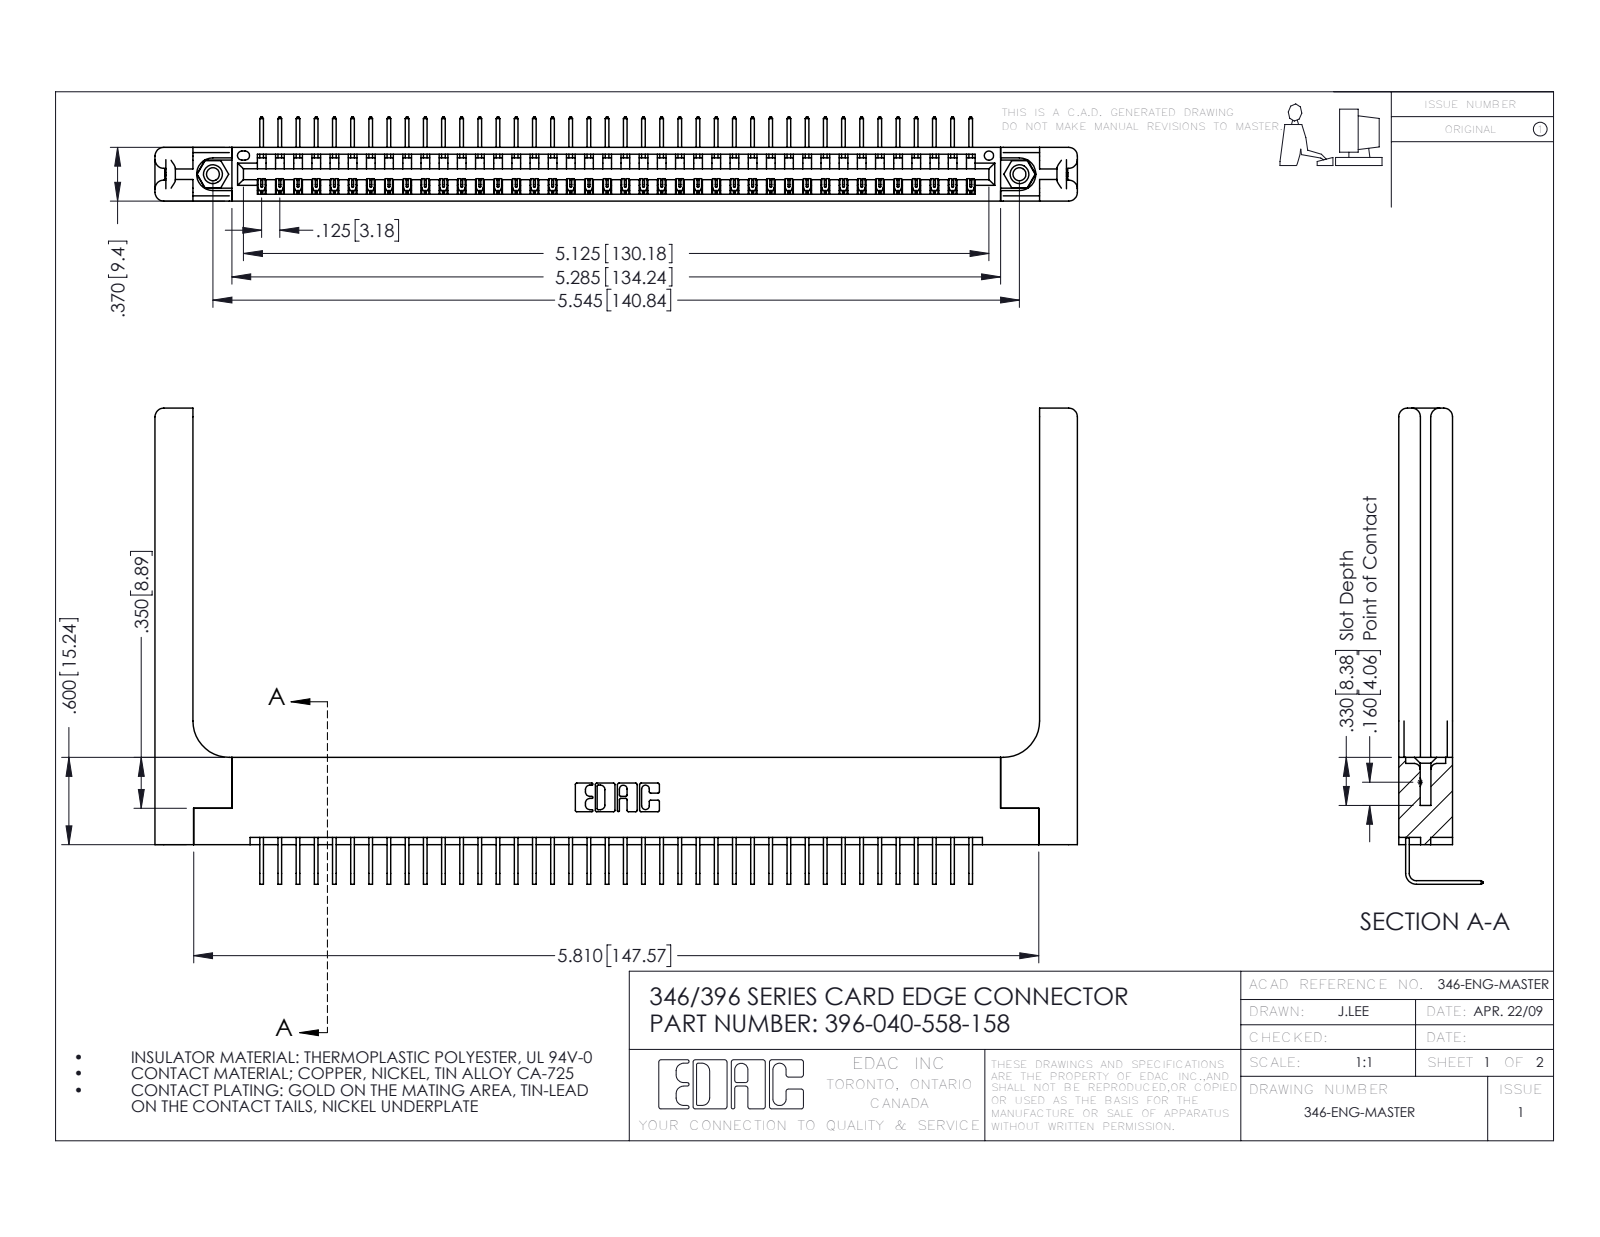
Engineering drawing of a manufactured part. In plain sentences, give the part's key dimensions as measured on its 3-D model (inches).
The part is named "396-040-558-158; 346-220-058_345-220-058; 345-292-001_558 Tail - 2; 346 Part_Flush Mounting Lugs - 0.156 Dia-TH (+1 more)". Its 3-D file was written by "SolidWorks 2016 (CONFIG_CONTROL_DESIGN)". It is 45 solids with 2778 faces: 1904 planar, 814 cylindrical and 60 other. Overall it measures 6.341 by 3.273 by 0.58 inches. Its volume is 1.407 cubic inches and its surface area 39.31 square inches. Round holes: 2 of diameter 0.089, 2 of diameter 0.125, 2 of diameter 0.156, 1 of diameter 0.064. Round bosses or shafts: 2 of diameter 0.155. Partial cylindrical surfaces (rounded edges, fillets, slot ends): 80 of radius 0.006, 22 of radius 0.01, 16 of radius 0.06, 6 of radius 0.007, 6 of radius 0.031, 3 of radius 0.026, 2 of radius 0.03, 2 of radius 0.031. The main face-to-face distances are 0.37, 0.322, 0.048, 0.072, 0.148, 0.15, 0.025, 0.298, 0.25, 0.222. The hole center spacings are 0.246, 5.336, 5.545.
